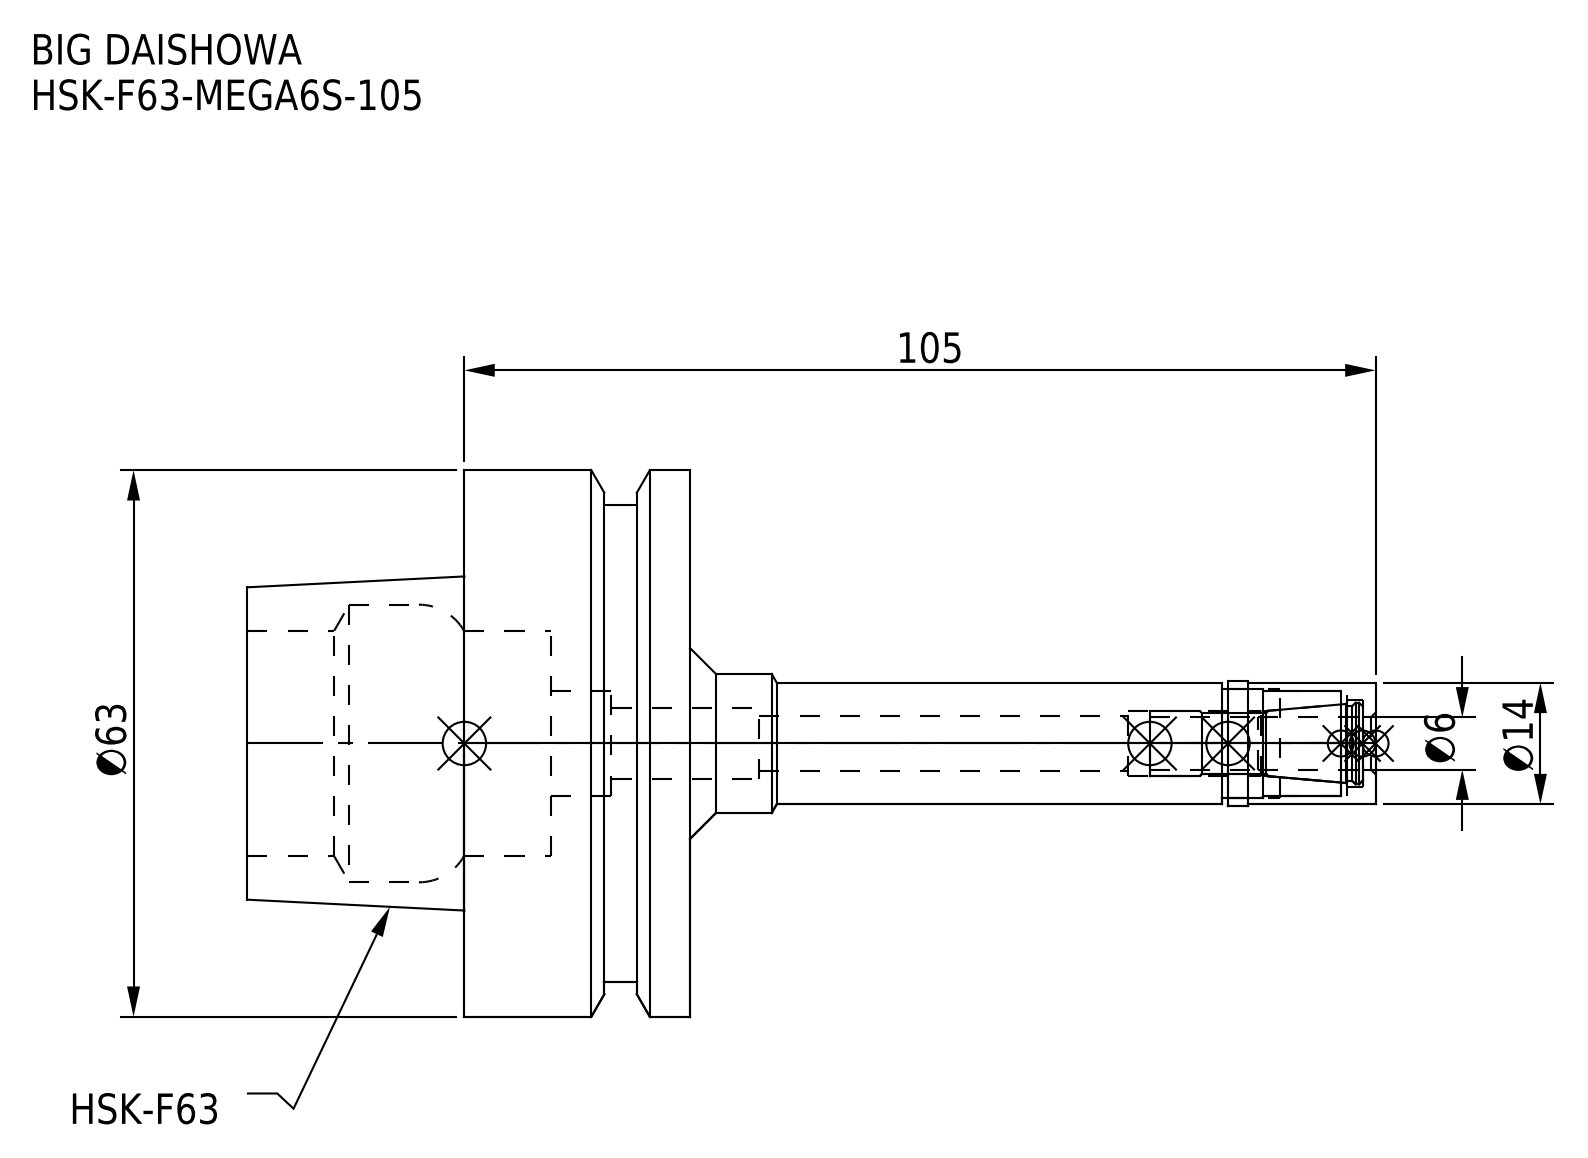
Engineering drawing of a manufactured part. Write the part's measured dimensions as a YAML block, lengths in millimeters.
part_name: "HF63MS06105-060_ASM.stp; HSK-F63-MEGA6S-105_1.stp; HSK-F63-MEGA6S-105-060-FreeParts; DXF_TEMP_ASSY_ASM_4_ASM.stp (+3 more)"
step_written_by: "SolidWorks 2019 (CONFIG_CONTROL_DESIGN)"
units: millimeters
bodies: {solids: 2, faces: 78, planar: 18, cylindrical: 42, other: 18}
overall_size: [130, 63, 63]
volume: 91171
surface_area: 25328
round_holes:
  - {diameter: 6.1, count: 1}
  - {diameter: 6.4, count: 1}
  - {diameter: 7.4, count: 1}
  - {diameter: 8.25, count: 1}
  - {diameter: 10, count: 1}
  - {diameter: 12, count: 1}
  - {diameter: 12.5, count: 1}
  - {diameter: 26, count: 1}
  - {diameter: 32, count: 1}
round_bosses_or_shafts:
  - {diameter: 63, count: 1}
  - {diameter: 55, count: 1}
  - {diameter: 16, count: 1}
  - {diameter: 14.3, count: 1}
  - {diameter: 14, count: 1}
face_to_face_distances: [26, 51, 25, 16.05, 9.95, 34.95, 6.12, 9.93, 19.88, 44.88]
